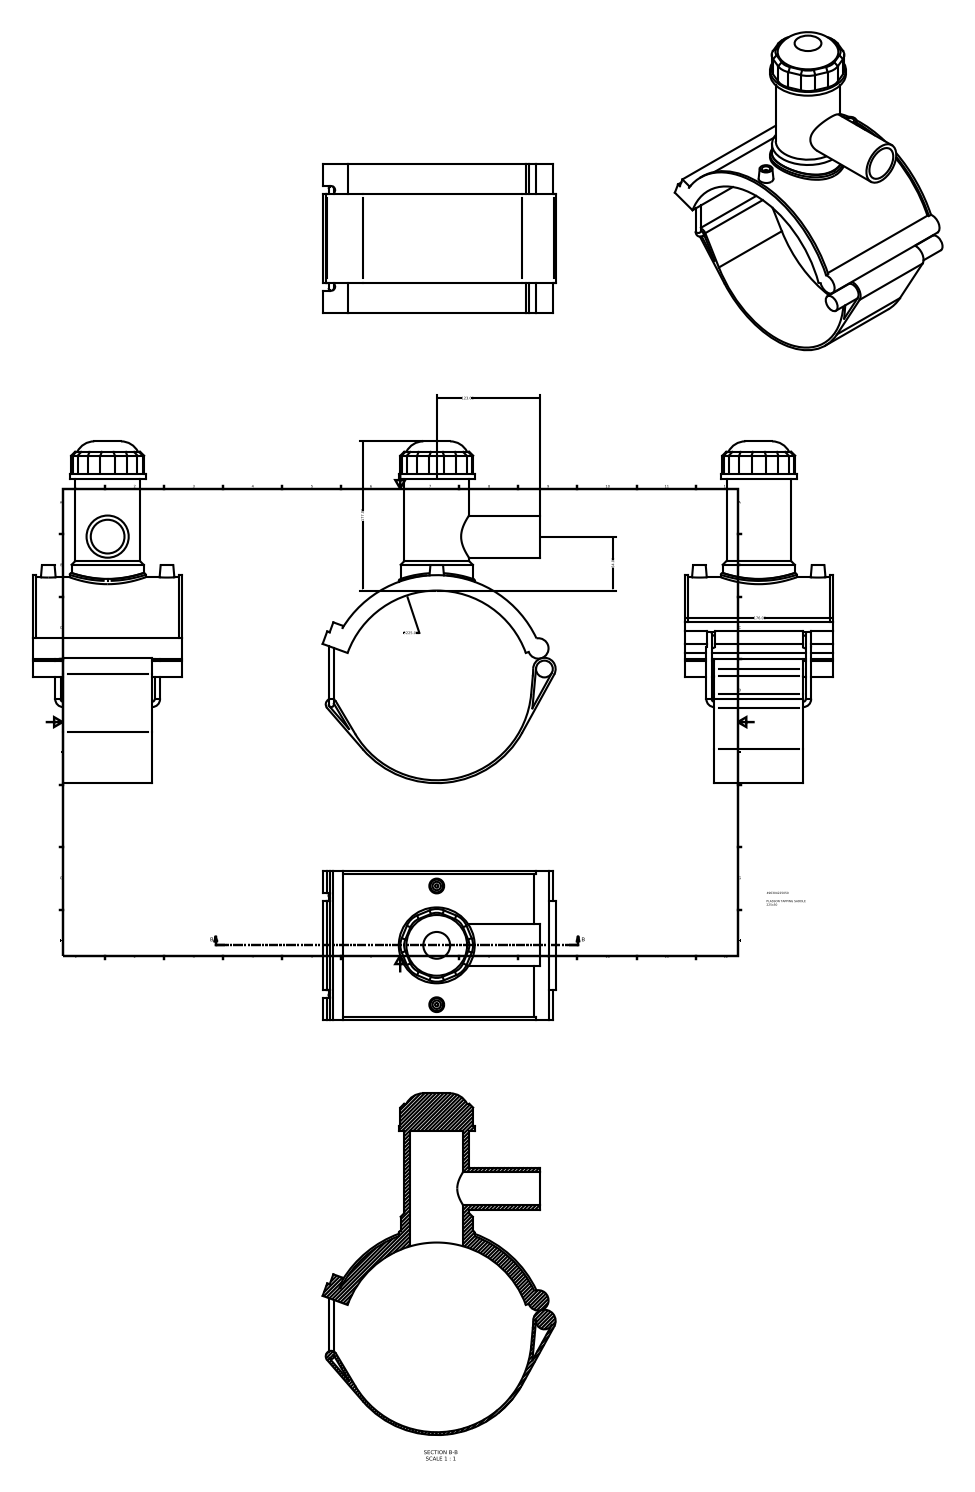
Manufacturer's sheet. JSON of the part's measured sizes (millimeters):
{"part_name": "496304225050", "step_written_by": "Autodesk Inventor 2015 (AUTOMOTIVE_DESIGN)", "units": "millimeters", "bodies": {"solids": 1, "faces": 121, "planar": 68, "cylindrical": 38, "other": 15}, "overall_size": [405.38, 276.37, 176], "volume_mm3": 1629000, "surface_area_mm2": 350099, "round_holes": [[10, 2], [40, 1], [63, 1]], "round_bosses_or_shafts": [[6.3, 2], [4, 2], [90, 1], [85.5, 1], [76.5, 1], [50, 1], [19.9, 1]], "partial_cylinders_radius": [[22.5, 8], [4.72, 2], [112.5, 2], [3.15, 1], [6.53, 1], [12.12, 1], [13.33, 1], [115.88, 1]], "face_to_face_distances": [176, 3.4, 3.38, 3.37, 35.2, 140.8, 3, 3.15, 28.35, 15.76], "hole_center_spacings": [70.4, 140.8]}
